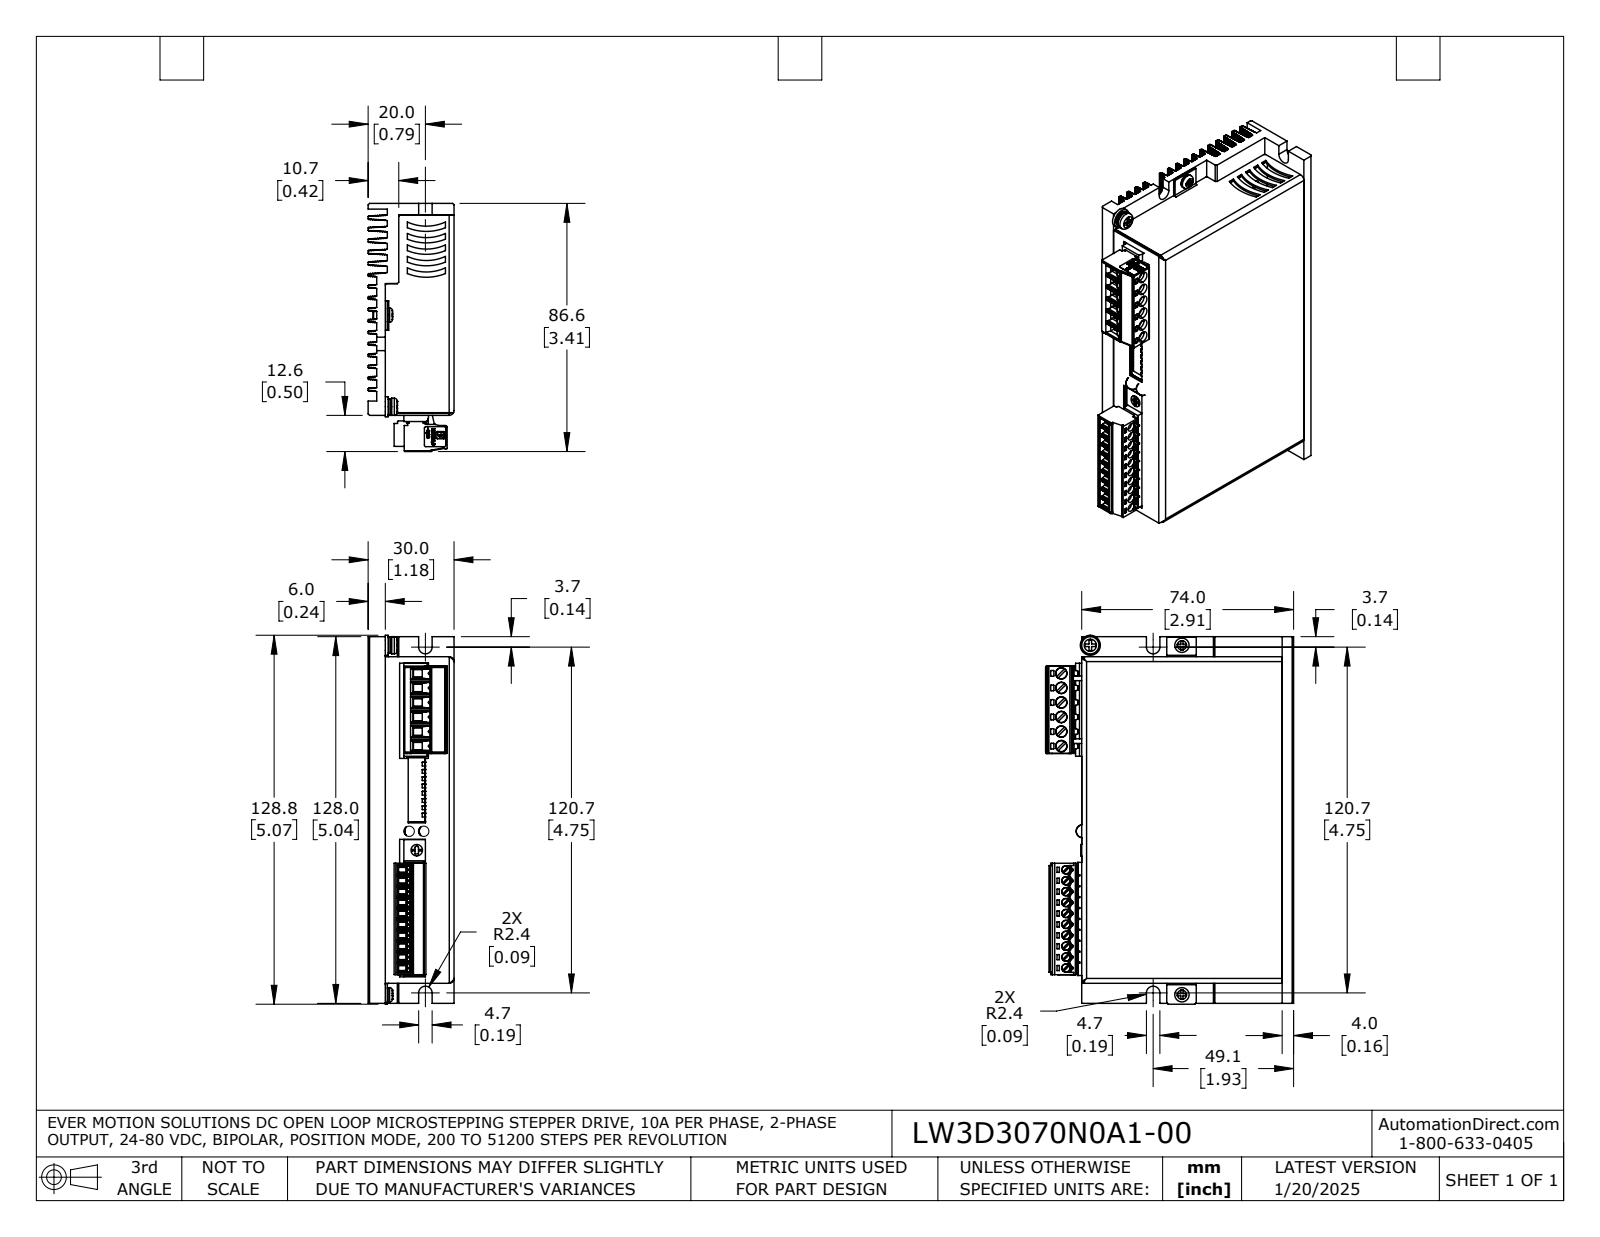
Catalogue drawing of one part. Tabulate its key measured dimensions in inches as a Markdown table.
| quantity | value |
| --- | --- |
| part name | LW3D3070N0A1-00 |
| STEP written by | SolidWorks 2021 (AUTOMOTIVE_DESIGN) |
| units | inches |
| bodies | 16 solids, 3049 faces (2109 planar, 687 cylindrical, 253 other) |
| overall size | 5.071 × 2.998 × 1.181 |
| volume | 5.076 in³ |
| surface area | 157.3 in² |
| round holes (diameter × count) | 0.03 × 36, 0.04 × 34, 0.049 × 10, 0.05 × 10, 0.081 × 9, 0.06 × 8, 0.106 × 7, 0.126 × 3, 0.047 × 2, 0.142 × 2, 0.098 × 1, 0.134 × 1 |
| round bosses / shafts (diameter × count) | 0.047 × 10, 0.063 × 9, 0.055 × 6, 0.11 × 5, 0.197 × 2, 0.098 × 2, 0.276 × 1, 0.236 × 1 |
| partial cylindrical surfaces (radius × count) | 0.006 × 236, 0.008 × 25, 0.006 × 10, 0.059 × 10, 0.118 × 6, 0.628 × 5, 0.7 × 5, 0.008 × 4 |
| main face-to-face distances | 0.028, 0.69, 0.917, 0.662, 0.753, 0.063, 0.725, 0.945, 0.255, 0.192 |
| hole center spacings | 0.1, 0.3, 0.2, 0.224, 0.316, 0.141, 0.15, 0.6 |
